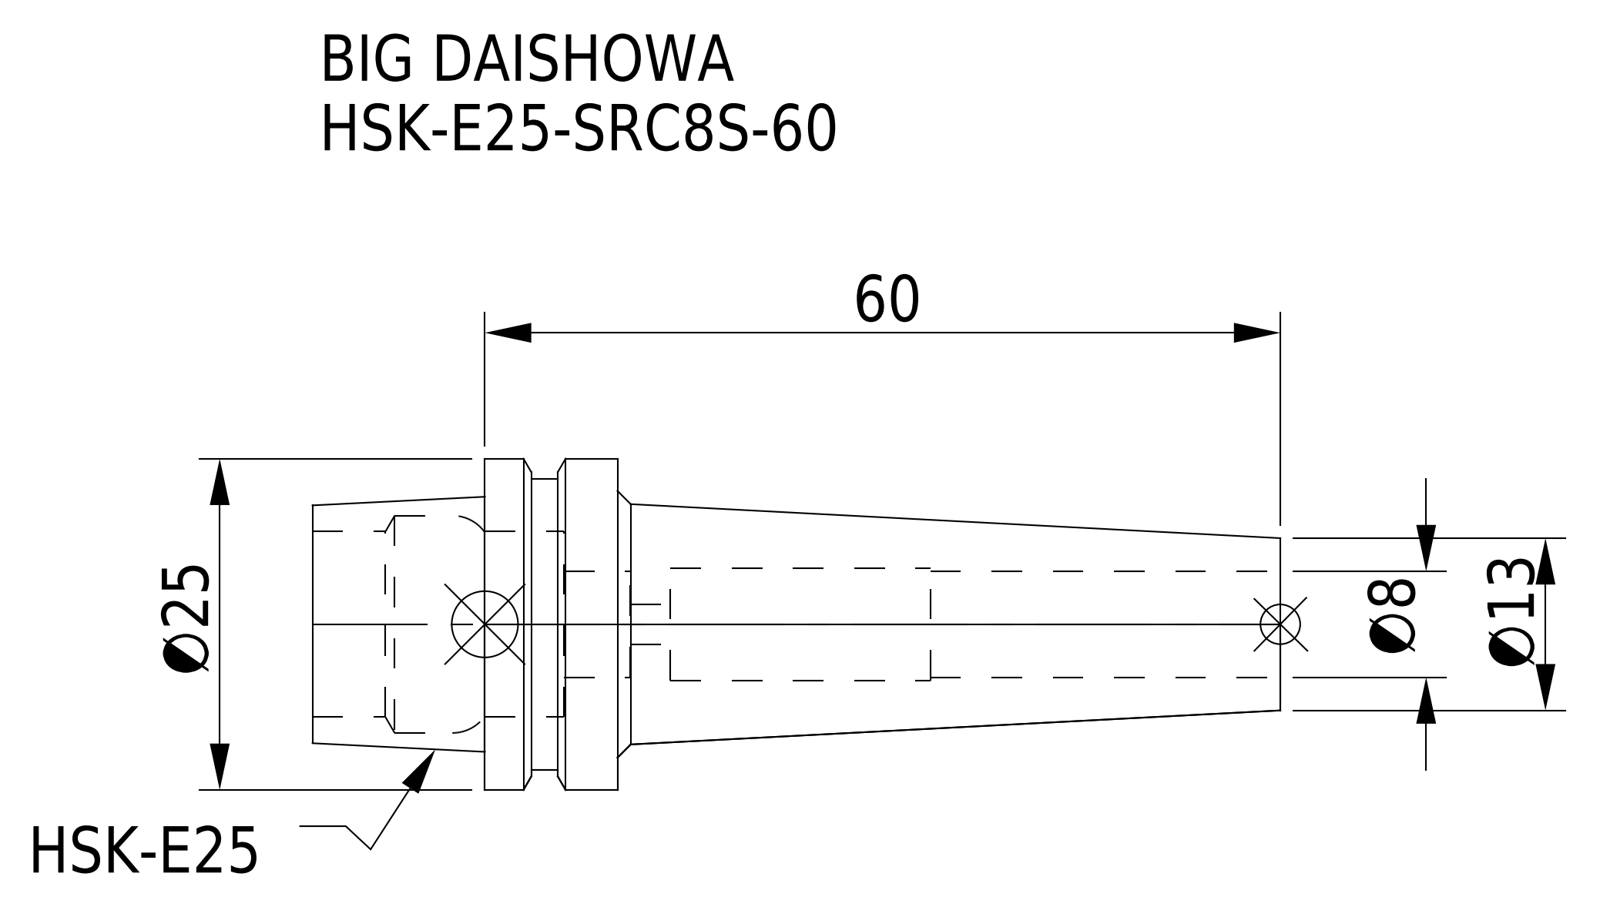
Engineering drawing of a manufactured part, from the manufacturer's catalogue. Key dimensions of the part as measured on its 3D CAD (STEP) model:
Part name (STEP PRODUCT): HSK-E25-SRC8S-60
STEP written by: CREO PARAMETRIC BY PTC INC, 2016380 (AUTOMOTIVE_DESIGN)
Units: millimetres
Bodies: 1 solid, 46 faces (10 planar, 22 cylindrical, 14 other)
Overall size (bounding box): 73 × 25 × 25
Volume: 11 882 mm³ · Surface area: 7 196 mm²
Round holes (diameter × count): ⌀3 ×1, ⌀8 ×1, ⌀8.5 ×1, ⌀14 ×1, ⌀16.4 ×1
Round bosses / shafts (diameter × count): ⌀25 ×1, ⌀22 ×1
Main face-to-face distances: 10, 4.05, 5.95, 23, 18.95, 13, 50, 54.05, 60, 73
